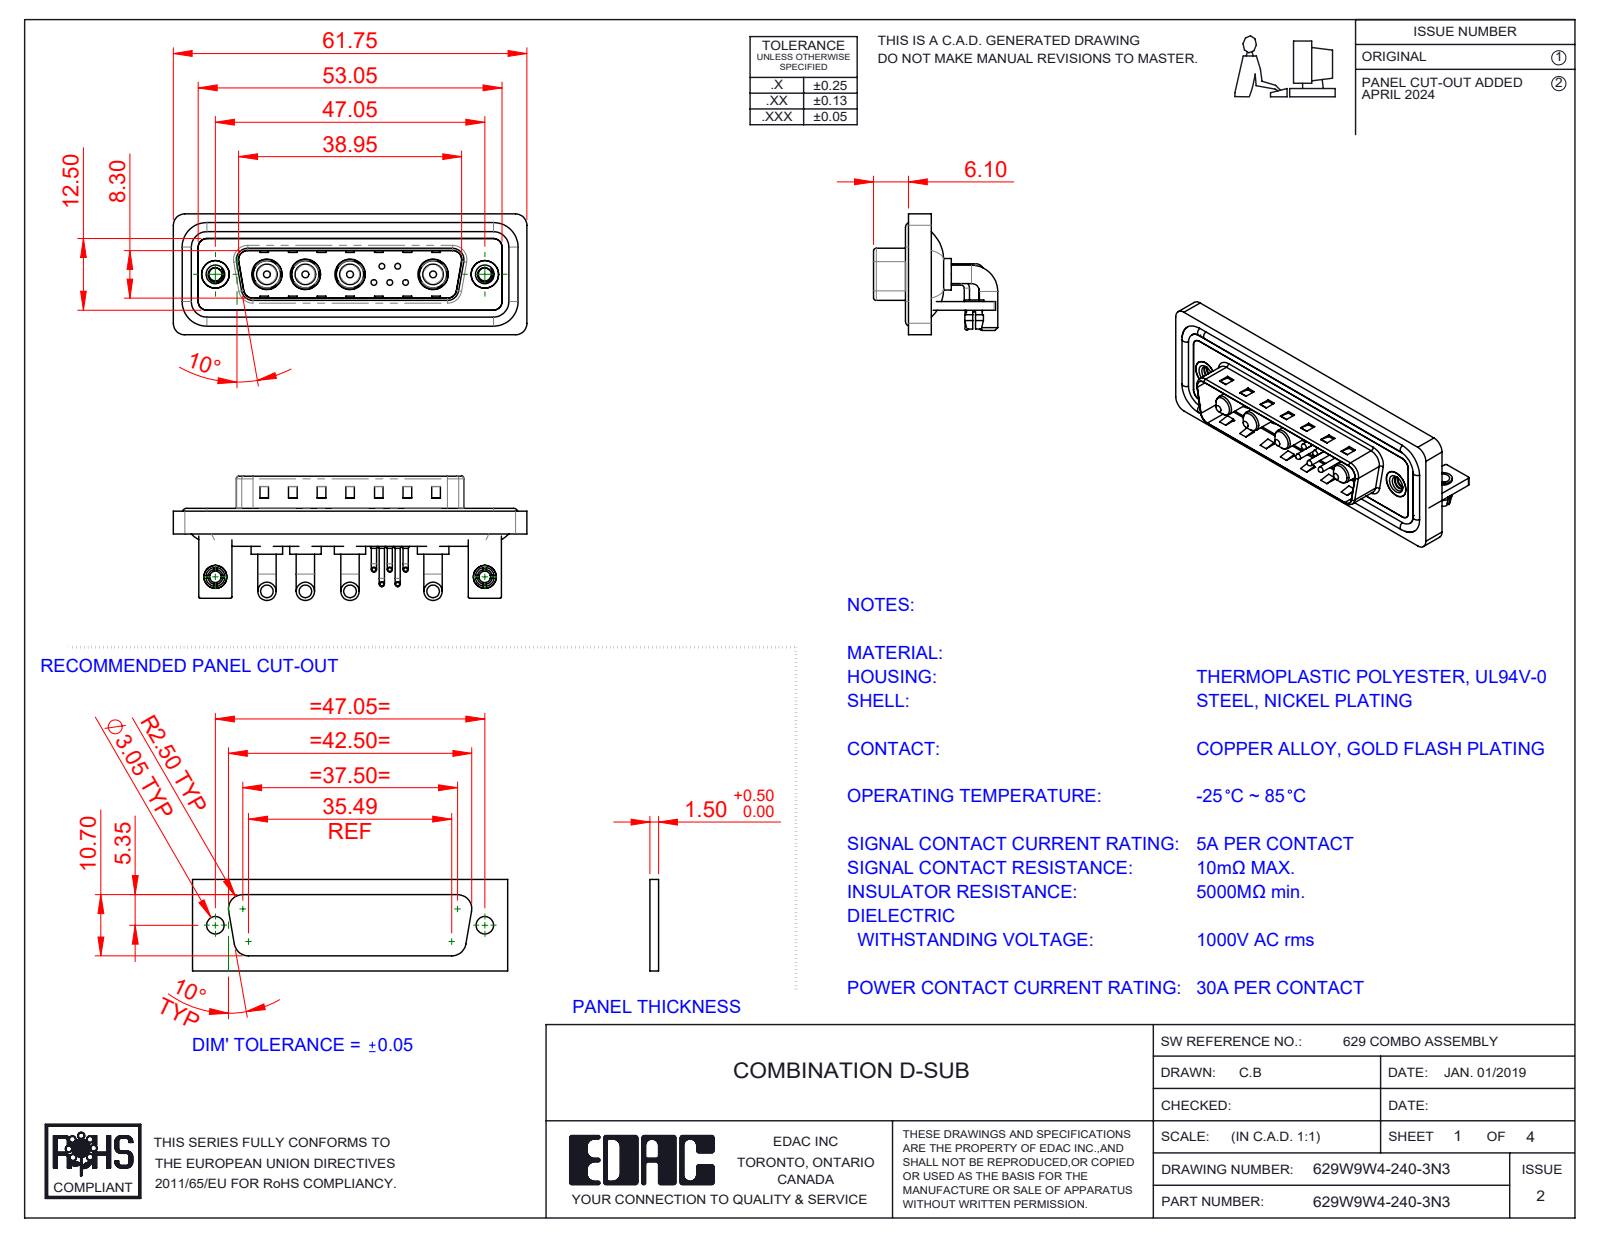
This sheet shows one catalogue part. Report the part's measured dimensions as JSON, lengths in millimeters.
{"part_name": "629Combo Housing_9W4; 629Combo Shell Rear_25 Contacts; 629Combo Contact Row 1; 629Combo Stabilizer Bracket (+7 more)", "step_written_by": "SolidWorks 2023 (CONFIG_CONTROL_DESIGN)", "units": "millimeters", "bodies": {"solids": 24, "faces": 1337, "planar": 637, "cylindrical": 502, "other": 198}, "overall_size": [61.75, 21.7, 21.1], "volume_mm3": 8130, "surface_area_mm2": 13248, "round_holes": [[2, 7], [0.75, 5], [1.6, 5], [4.85, 4], [5.3, 4], [2.26, 2], [2.5, 2], [3.2, 2], [4, 2], [4.8, 2], [5, 2]], "round_bosses_or_shafts": [[0.9, 10], [3.2, 8], [1.5, 5], [1, 5], [0.65, 5], [5.5, 4], [5.2, 4], [4.75, 4]], "partial_cylinders_radius": [[2, 19], [1.5, 18], [0.25, 16], [0.5, 9], [1.6, 8], [1.01, 5], [0.6, 4], [0.65, 4]], "face_to_face_distances": [0.4, 1.5, 0.8, 2.9, 2.1, 1.1, 3.7, 4.1, 4.5, 1.6], "hole_center_spacings": [3.16, 2.77, 5.04, 14.5, 47.05, 2.78, 4.4, 4.41]}
